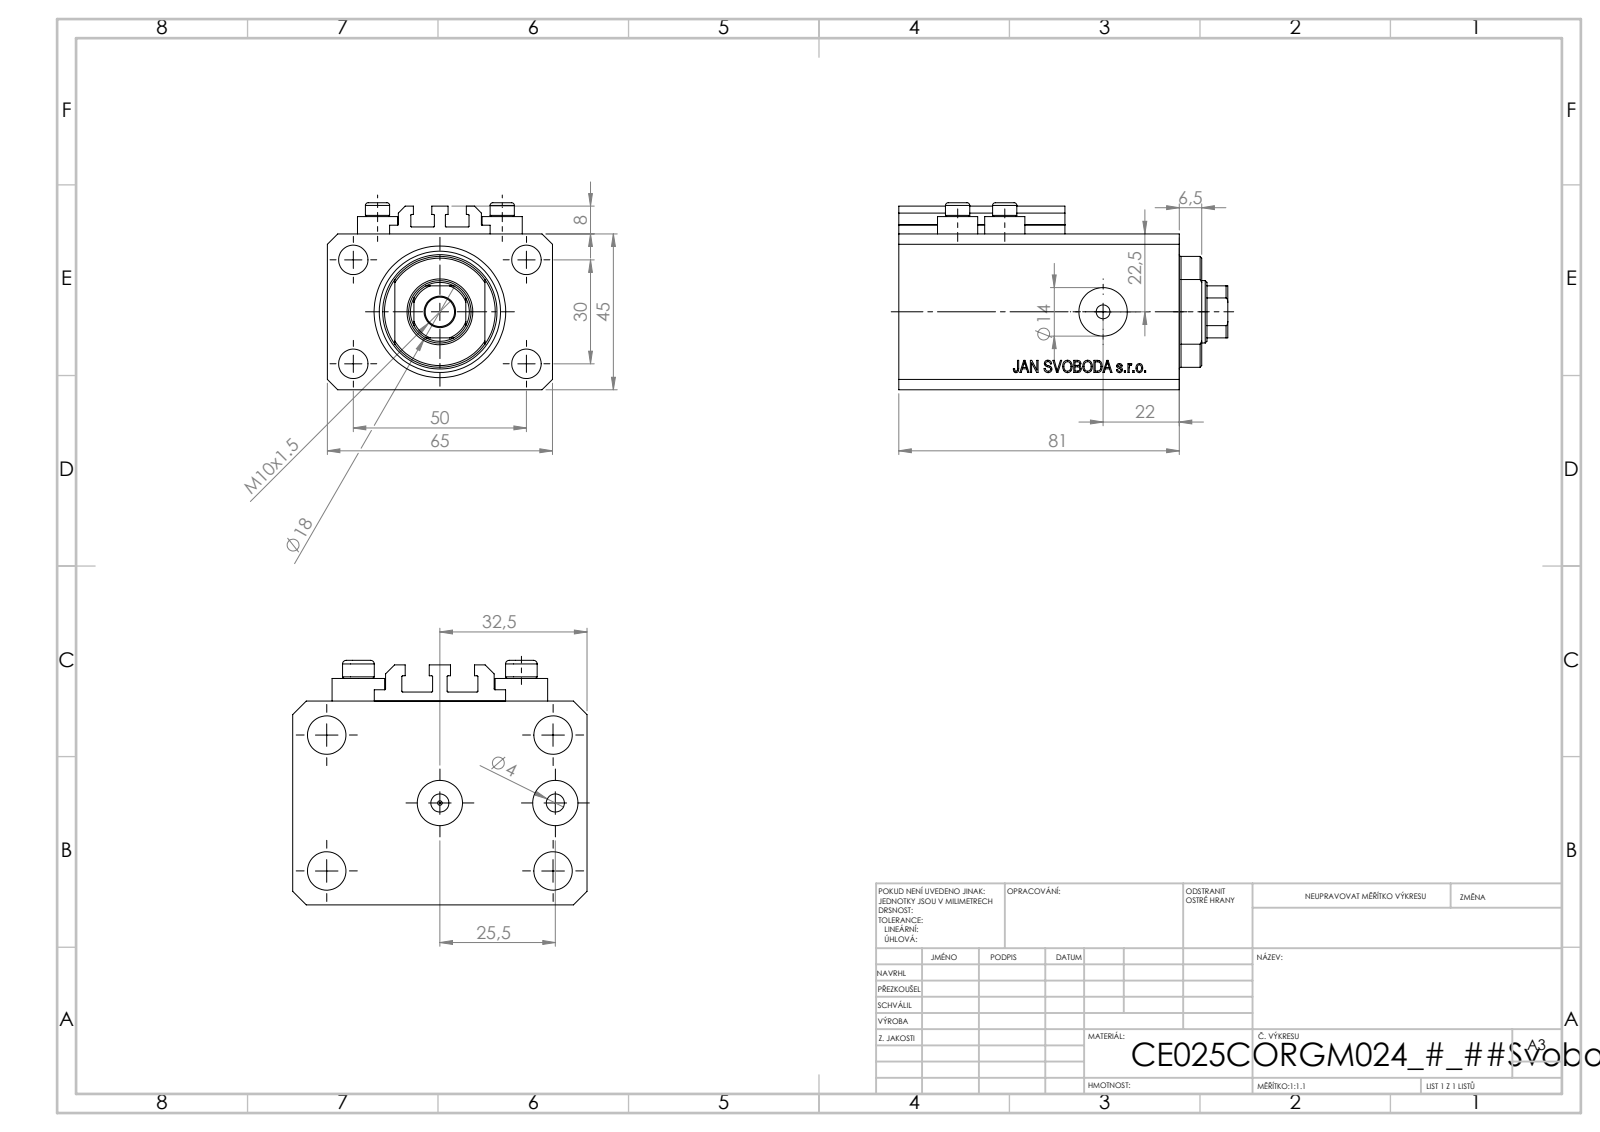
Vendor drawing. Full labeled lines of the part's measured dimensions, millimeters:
Part name (STEP PRODUCT): V250CE_C_Body; ALLEN BOLT V250CE; V250CE_C_VCP; V250CE_VC_C
STEP written by: SolidWorks 2019 (CONFIG_CONTROL_DESIGN)
Units: millimetres
Bodies: 8 solids, 1042 faces (504 planar, 92 cylindrical, 446 other)
Overall size (bounding box): 95 × 65 × 54
Volume: 221 780 mm³ · Surface area: 59 903 mm²
Round holes (diameter × count): ⌀4 ×8, ⌀8.5 ×5, ⌀10 ×2, ⌀14 ×2, ⌀1.25 ×1, ⌀18 ×1, ⌀25 ×1, ⌀38 ×1
Round bosses / shafts (diameter × count): ⌀11.6 ×4, ⌀7 ×4
Partial cylindrical surfaces — rounded edges, fillets, slot ends (radius × count): R0.2 ×10, R8.5 ×1, R16 ×1
Main face-to-face distances: 45, 65, 14, 81, 67, 47, 6.9, 60.1, 74.1, 3
Hole centre spacings: 29.15, 13.6, 15.01, 30, 36, 38.48, 50, 52.68
